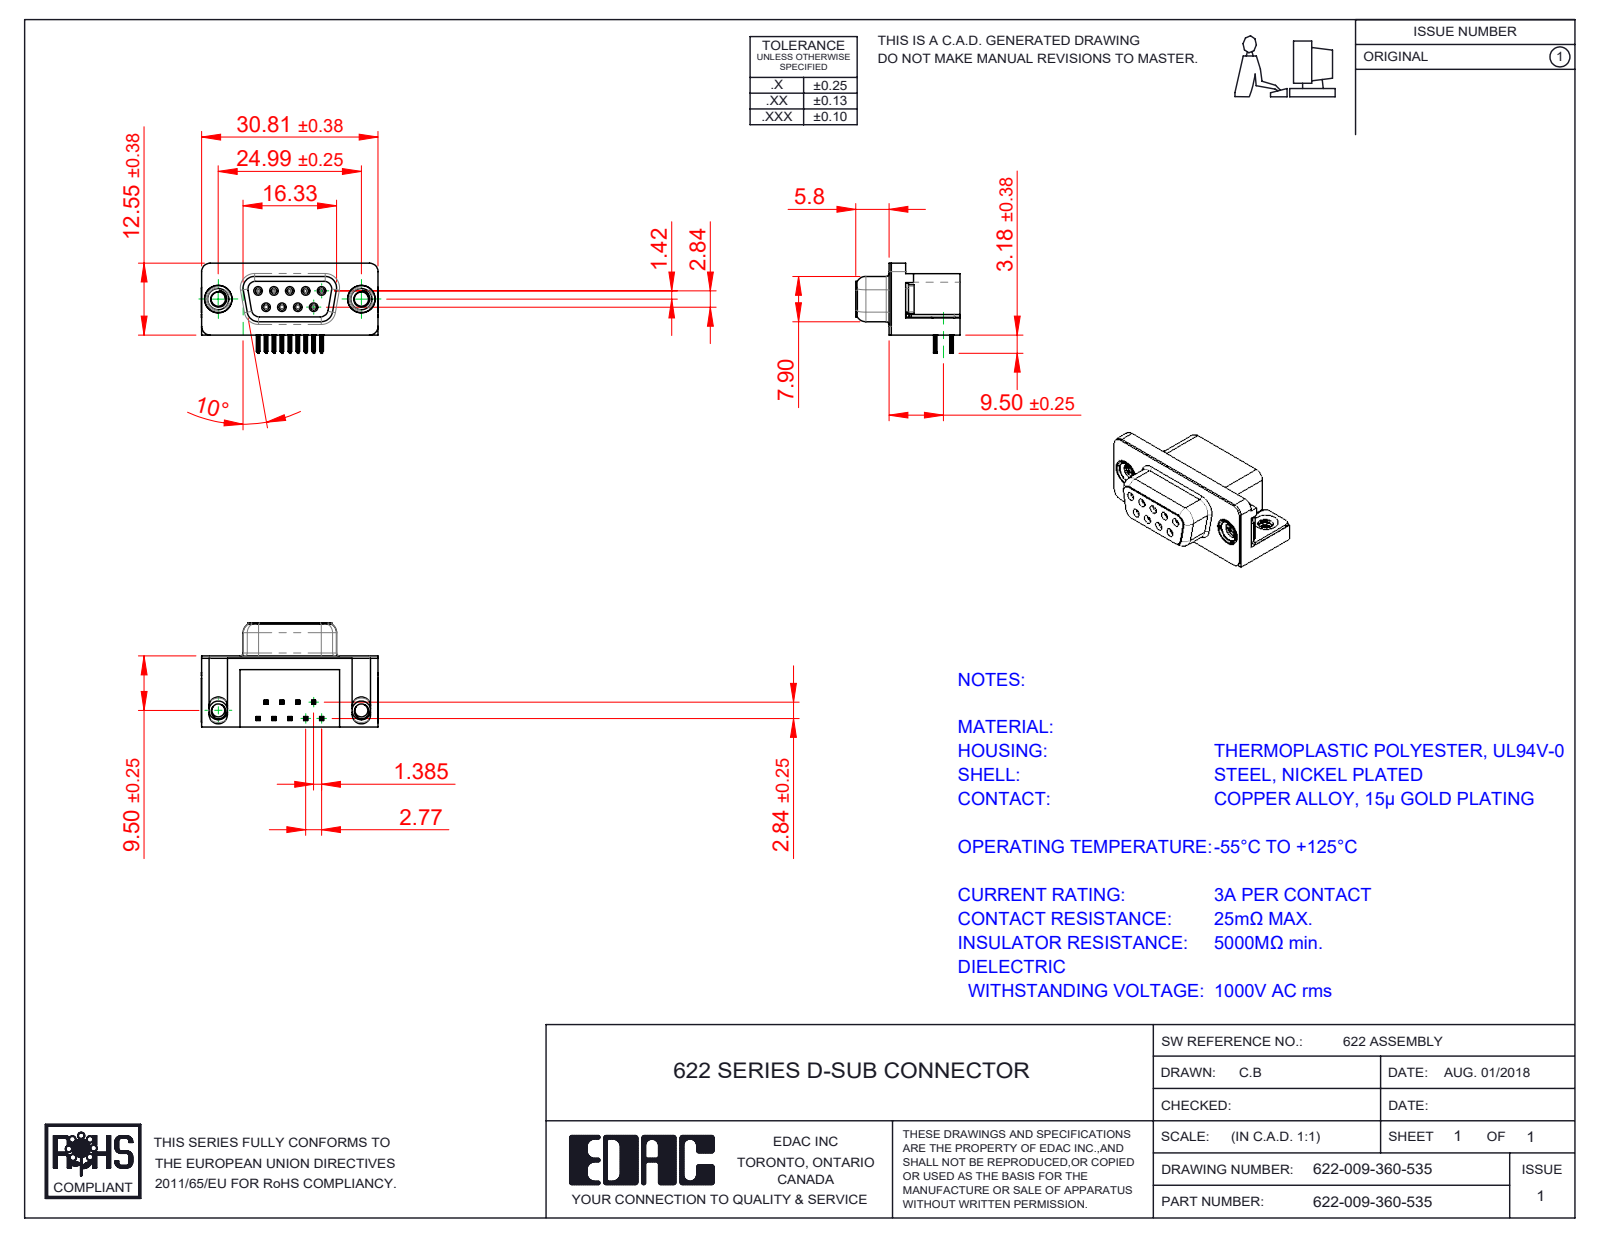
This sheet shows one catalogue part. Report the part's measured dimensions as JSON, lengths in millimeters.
{"part_name": "622 M3 Threaded Rivet; 622 Contact Top; 622-009-360-535; 622 Housing_9 Socket (+3 more)", "step_written_by": "SolidWorks 2016 (CONFIG_CONTROL_DESIGN)", "units": "millimeters", "bodies": {"solids": 15, "faces": 1612, "planar": 716, "cylindrical": 428, "other": 468}, "overall_size": [30.89, 18.2, 16.25], "volume_mm3": 3720, "surface_area_mm2": 5082, "round_holes": [[0.8, 9], [0.9, 9], [2.5, 2], [4, 2], [4.8, 2], [5, 2]], "round_bosses_or_shafts": [[1.2, 9], [4.9, 2], [4.75, 2], [3.9, 2]], "partial_cylinders_radius": [[0.1, 72], [0.15, 36], [0.35, 18], [1, 18], [0.5, 10], [0.34, 9], [0.25, 8], [1.35, 8]], "face_to_face_distances": [0.4, 12, 12.4, 0.35, 2.9, 2.5, 6.2, 10.34, 0.5, 9.5], "hole_center_spacings": [3.16, 2.77, 5.54, 5.03, 5.04, 8.31, 7.48, 7.49]}
